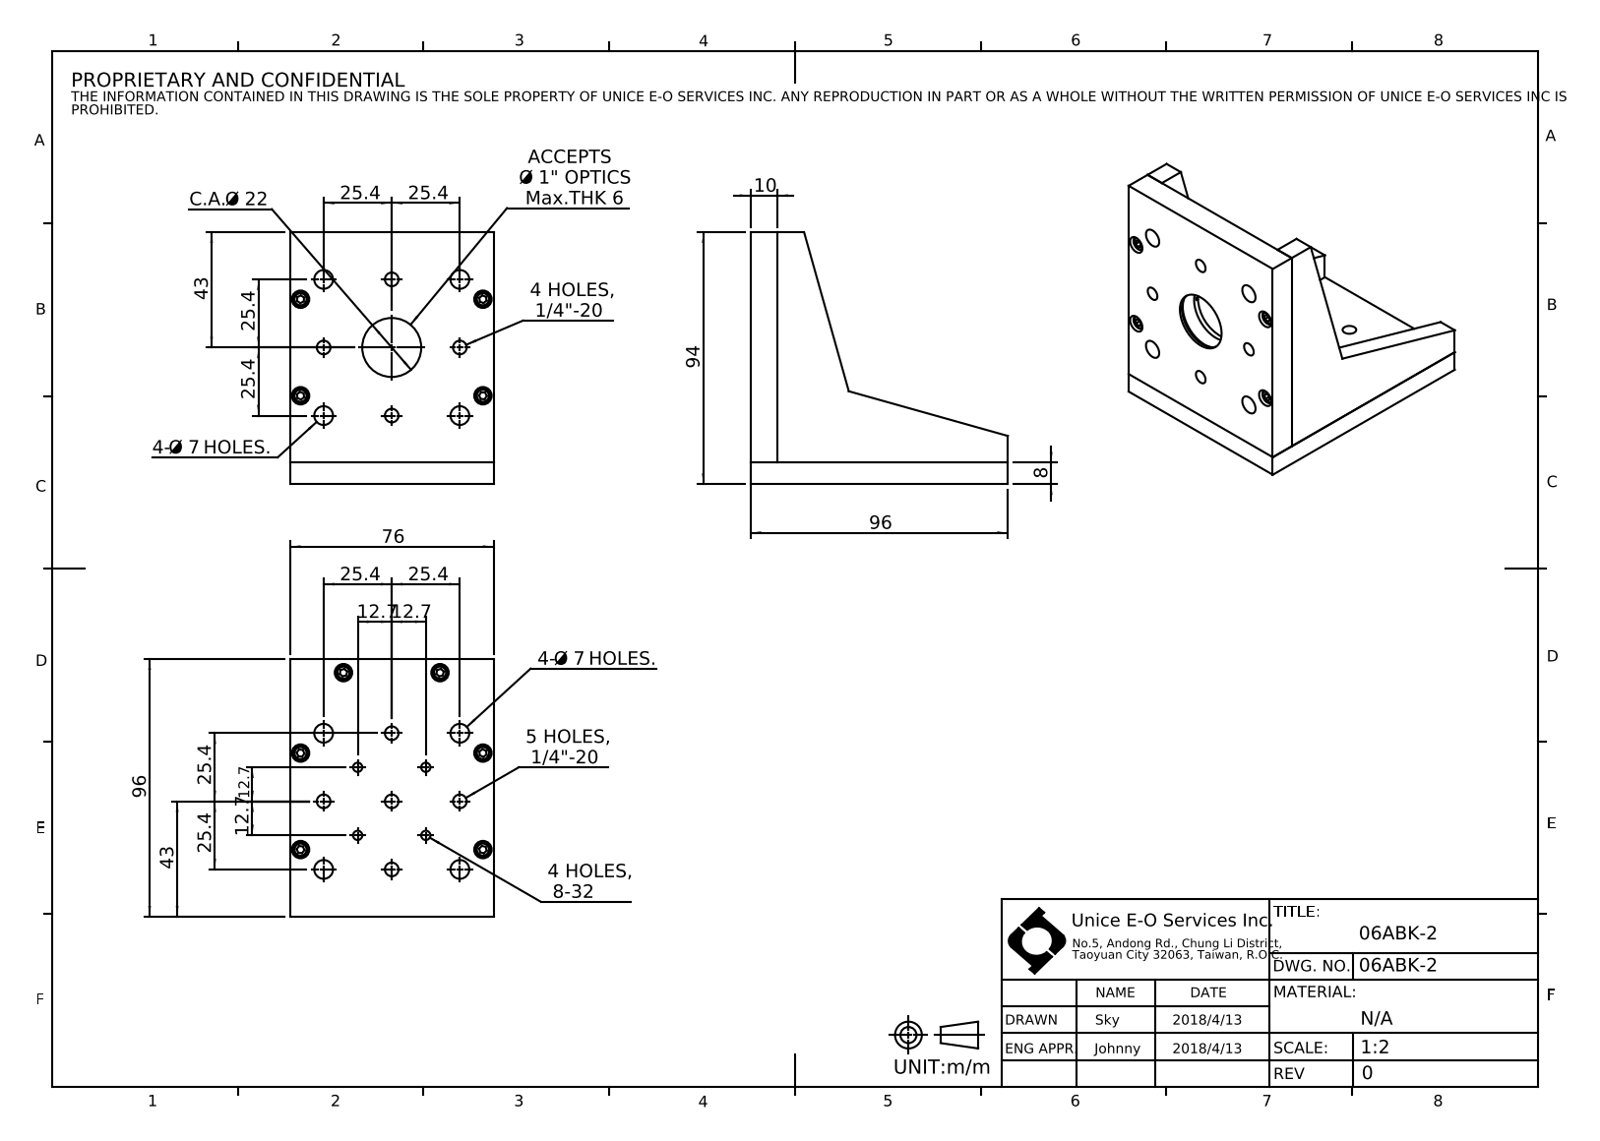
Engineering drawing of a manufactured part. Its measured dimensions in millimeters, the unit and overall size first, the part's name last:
Units: millimetres
Overall size (bounding box): 96 × 94 × 76
Round holes (diameter × count): ⌀2.5 ×10, ⌀3.4 ×10, ⌀6.5 ×10, ⌀5.11 ×9, ⌀7 ×8, ⌀3.45 ×4, ⌀22 ×1, ⌀23 ×1, ⌀25.7 ×1
Round bosses / shafts (diameter × count): ⌀5.5 ×10, ⌀3 ×10, ⌀26.93 ×1, ⌀25 ×1
Main face-to-face distances: 8, 10, 7.5, 68.5, 76, 61, 86, 94, 4, 96
Hole centre spacings: 25.4, 35.92, 17.96, 40.16, 56.8, 50.8, 11.35, 19.95
Volume: 156 637 mm³ · Surface area: 56 908 mm²
Bodies: 16 solids, 1174 faces (200 planar, 394 cylindrical, 580 other)
Part name (STEP PRODUCT): 06ABK-2
STEP written by: SolidWorks 2016 (CONFIG_CONTROL_DESIGN)
